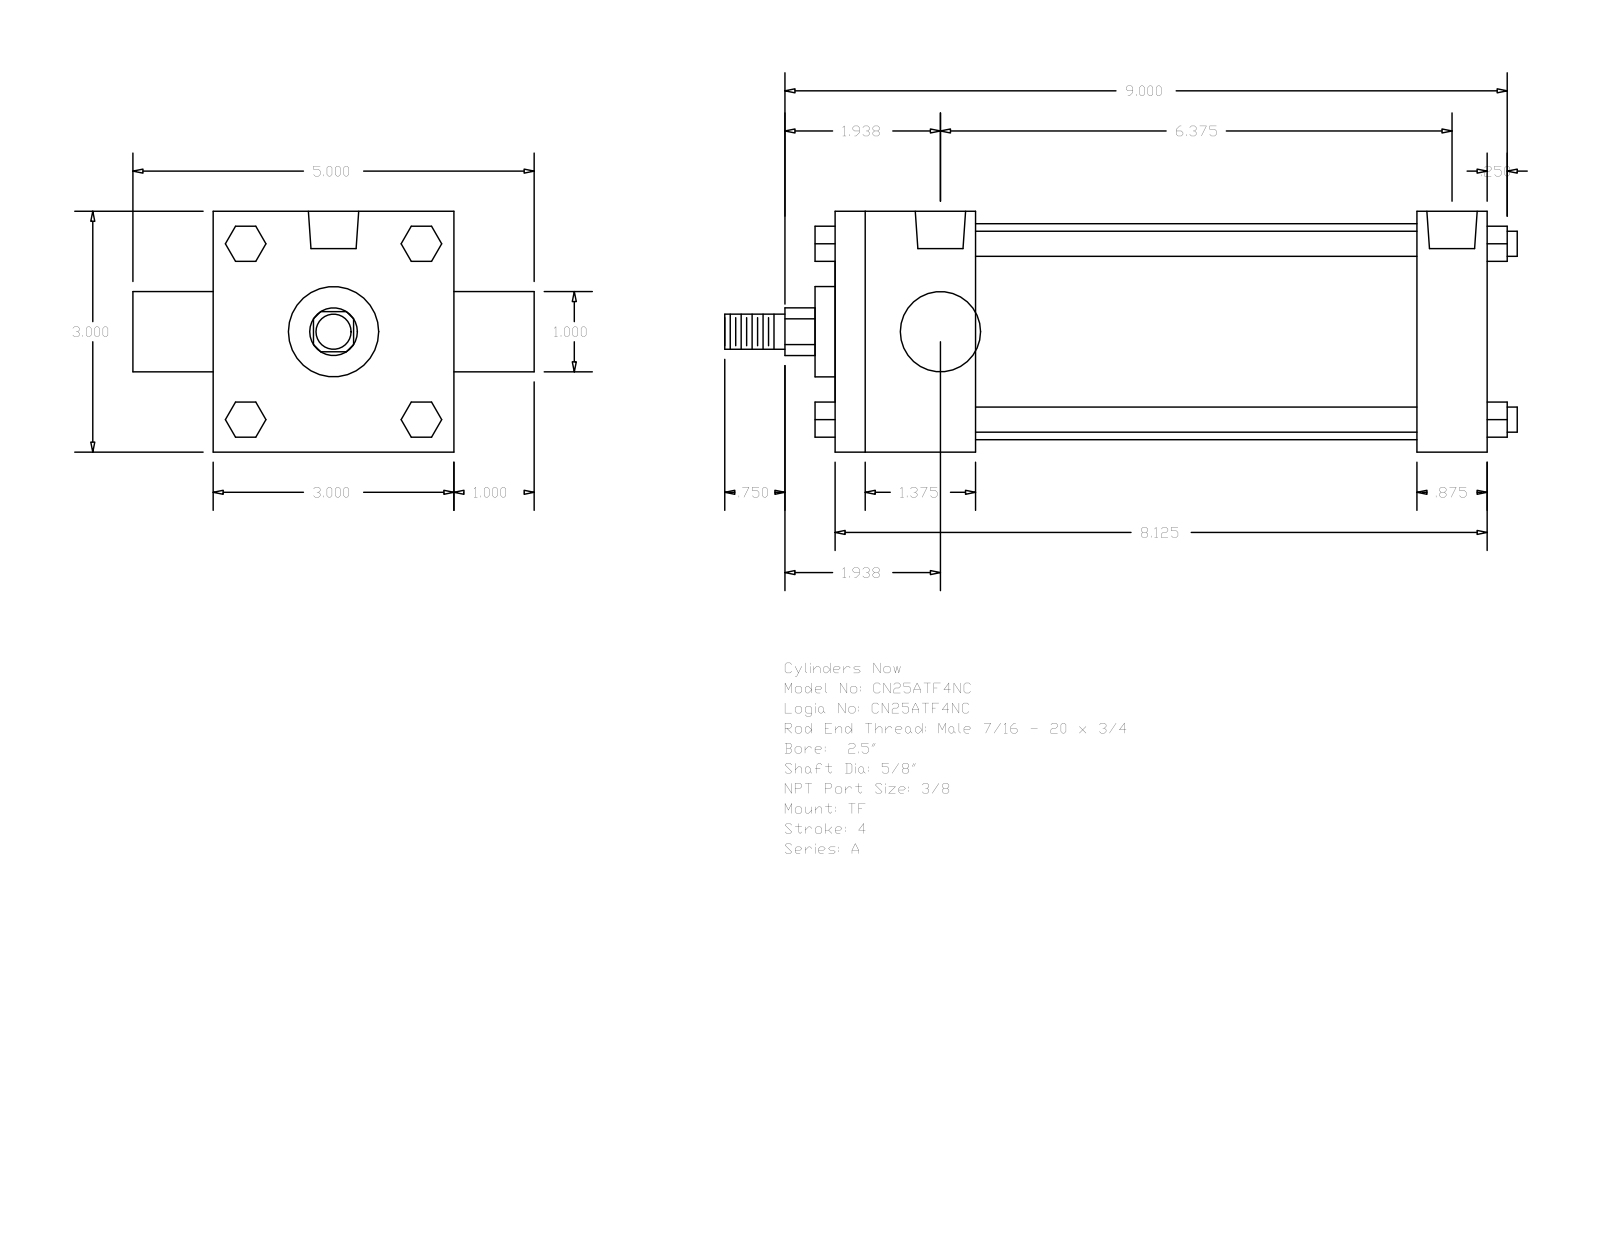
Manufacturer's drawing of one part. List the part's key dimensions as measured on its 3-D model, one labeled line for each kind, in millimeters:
Part name (STEP PRODUCT): A_TF__0250_0.625
STEP written by: GSSL Pune (CONFIG_CONTROL_DESIGN)
Units: millimetres
Bodies: 0 solids, 120 faces (92 planar, 28 cylindrical, 0 other)
Overall size (bounding box): 250.82 × 127 × 76.2
Round holes (diameter × count): ⌀5.56 ×3, ⌀15.93 ×2
Round bosses / shafts (diameter × count): ⌀7.94 ×4, ⌀68.33 ×1, ⌀28.57 ×1, ⌀25.4 ×1, ⌀15.88 ×1, ⌀11.11 ×1
Partial cylindrical surfaces — rounded edges, fillets, slot ends (radius × count): R7.54 ×1
Main face-to-face distances: 76.2, 206.37, 44.45, 184.15, 139.7, 161.92, 22.22, 25.4, 101.6, 6.35
Hole centre spacings: 2.38, 164.31, 161.93, 166.69
